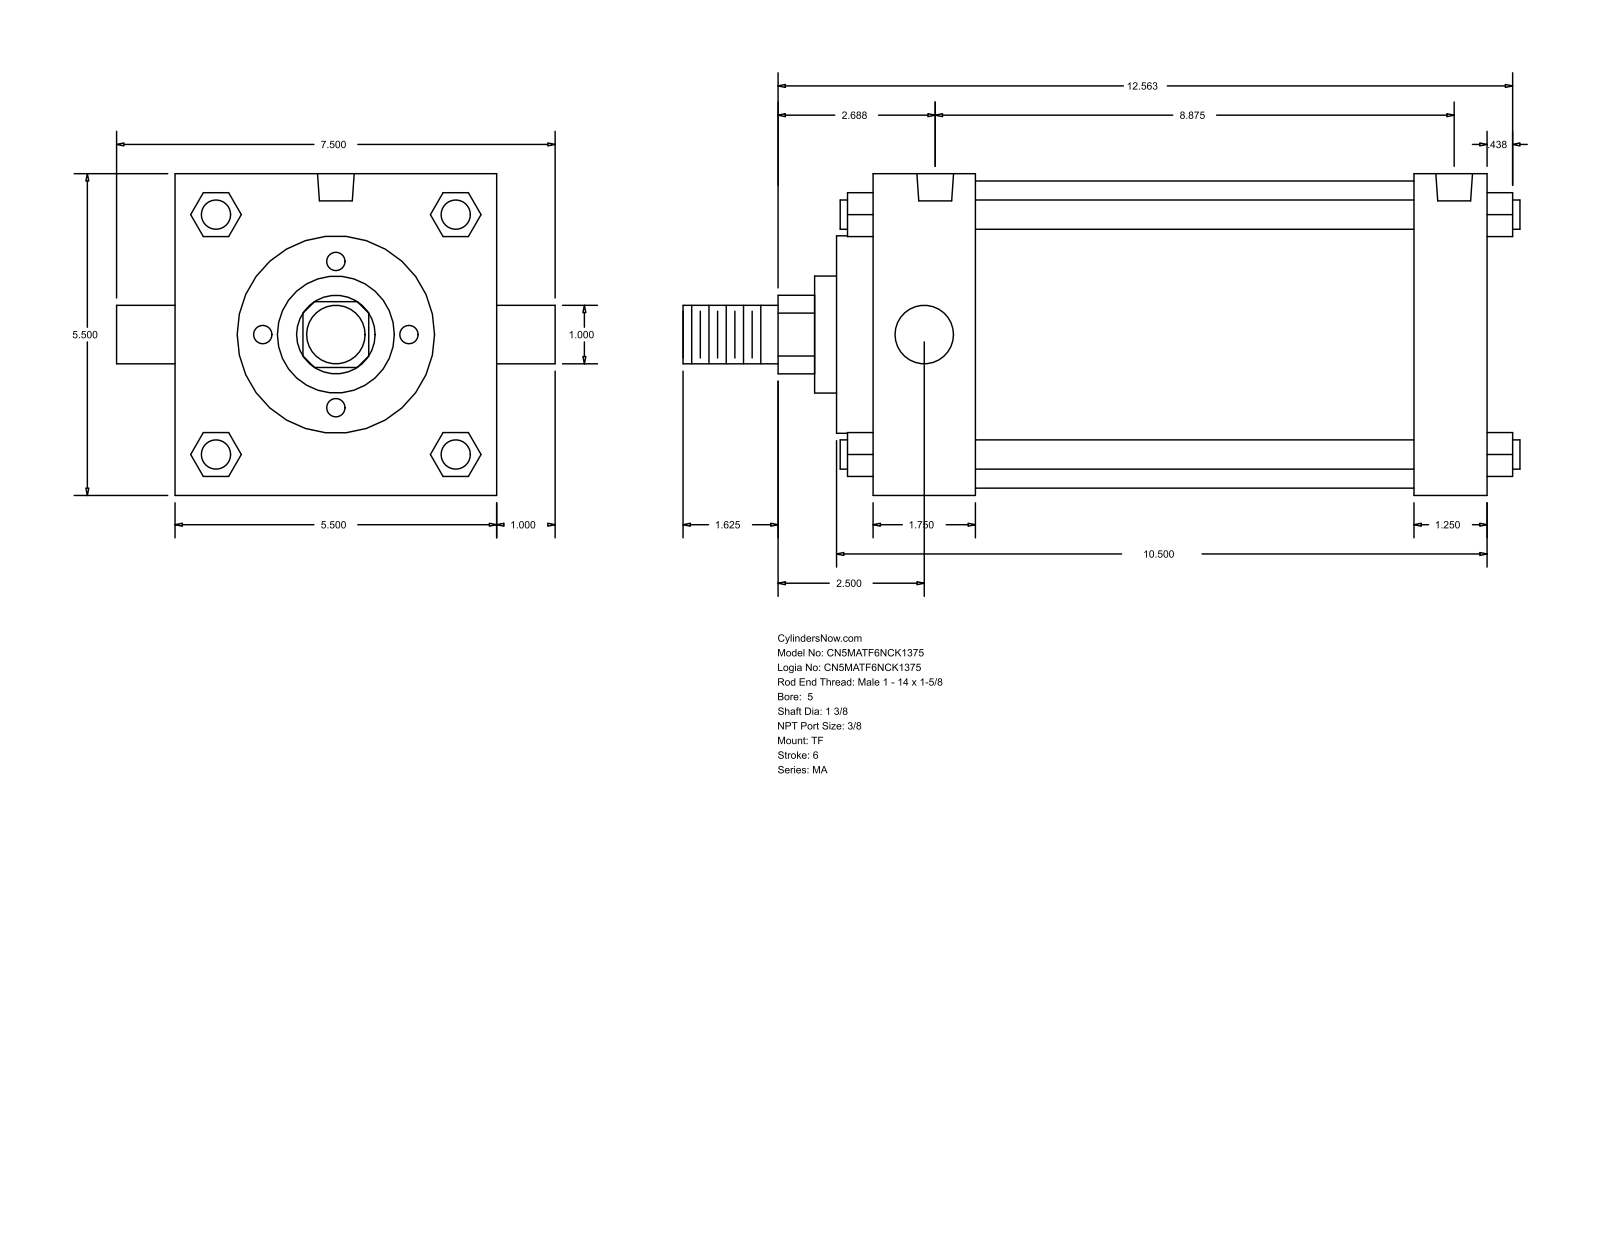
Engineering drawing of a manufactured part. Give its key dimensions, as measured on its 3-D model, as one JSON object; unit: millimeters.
{"part_name": "MA_TF__0500_1.375", "step_written_by": "GSSL Pune (CONFIG_CONTROL_DESIGN)", "units": "millimeters", "bodies": {"solids": 0, "faces": 122, "planar": 93, "cylindrical": 29, "other": 0}, "overall_size": [363.54, 190.5, 139.7], "round_holes": [[11.11, 3], [15.93, 2]], "round_bosses_or_shafts": [[12.7, 4], [25.4, 2], [133.35, 1], [85.72, 1], [50.8, 1], [34.92, 1]], "partial_cylinders_radius": [[17.06, 1]], "face_to_face_distances": [139.7, 266.71, 234.96, 31.75, 44.45, 190.51, 222.26, 15.87, 60.32, 250.83], "hole_center_spacings": [4.76, 4.77, 215.9, 220.66, 220.67, 225.43]}
